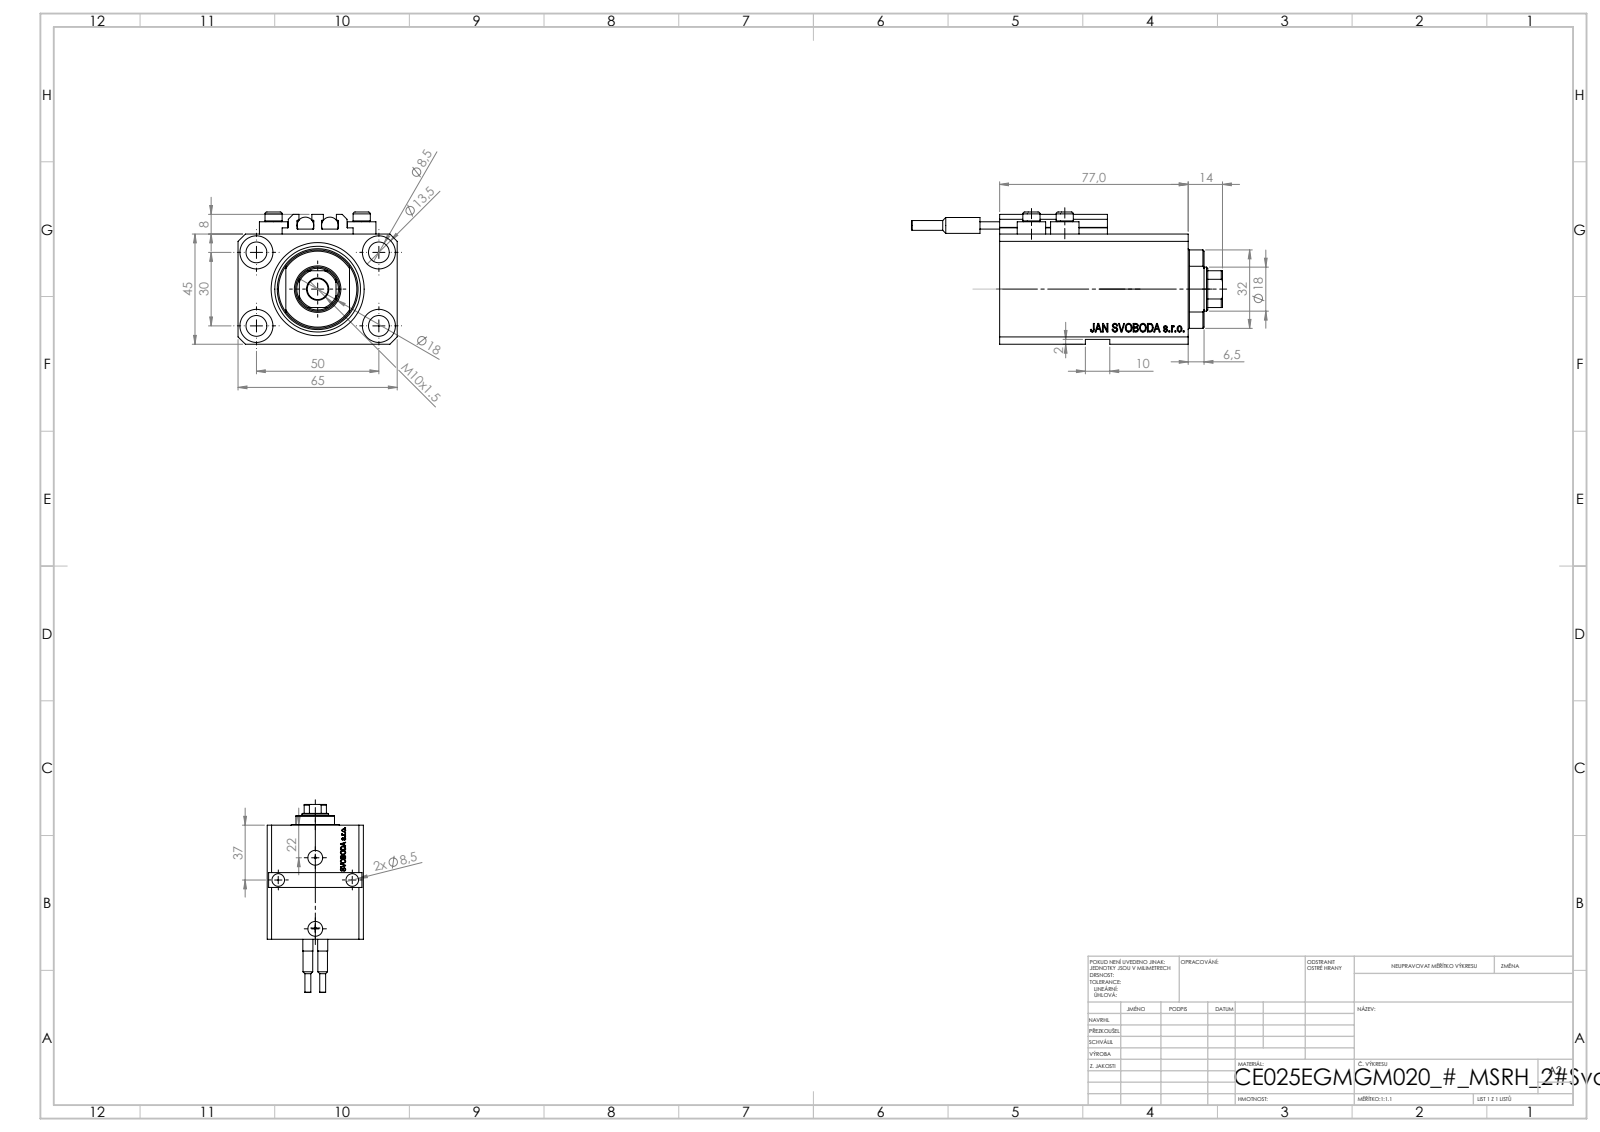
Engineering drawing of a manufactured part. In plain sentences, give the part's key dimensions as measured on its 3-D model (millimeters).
The part is named "SWITCH_V250CE; ALLEN BOLT V250CE; V250CE_C_VCP; V250CE_E_Body (+1 more)". Its 3-D file was written by "SolidWorks 2019 (CONFIG_CONTROL_DESIGN)". It is 10 solids with 1119 faces: 543 planar, 138 cylindrical and 438 other. Overall it measures 127 by 65 by 54 millimeters. Its volume is 203 348 cubic millimeters and its surface area 61 935 square millimeters. Round holes: 7 of diameter 8.5, 4 of diameter 1.25, 4 of diameter 4, 4 of diameter 13.5, 2 of diameter 10, 2 of diameter 13.16, 2 of diameter 20, 1 of diameter 18, 1 of diameter 25, 1 of diameter 38. Round bosses or shafts: 4 of diameter 11.6, 4 of diameter 7, 2 of diameter 6.8, 2 of diameter 6.5, 2 of diameter 4. Partial cylindrical surfaces (rounded edges, fillets, slot ends): 10 of radius 0.2, 1 of radius 8.5, 1 of radius 16. The main face-to-face distances are 45, 65, 63, 2, 14, 3, 77, 47, 5, 6.9. The hole center spacings are 29.15, 50, 13.6, 15.12, 18.81, 18.97, 26.22, 26.61.
